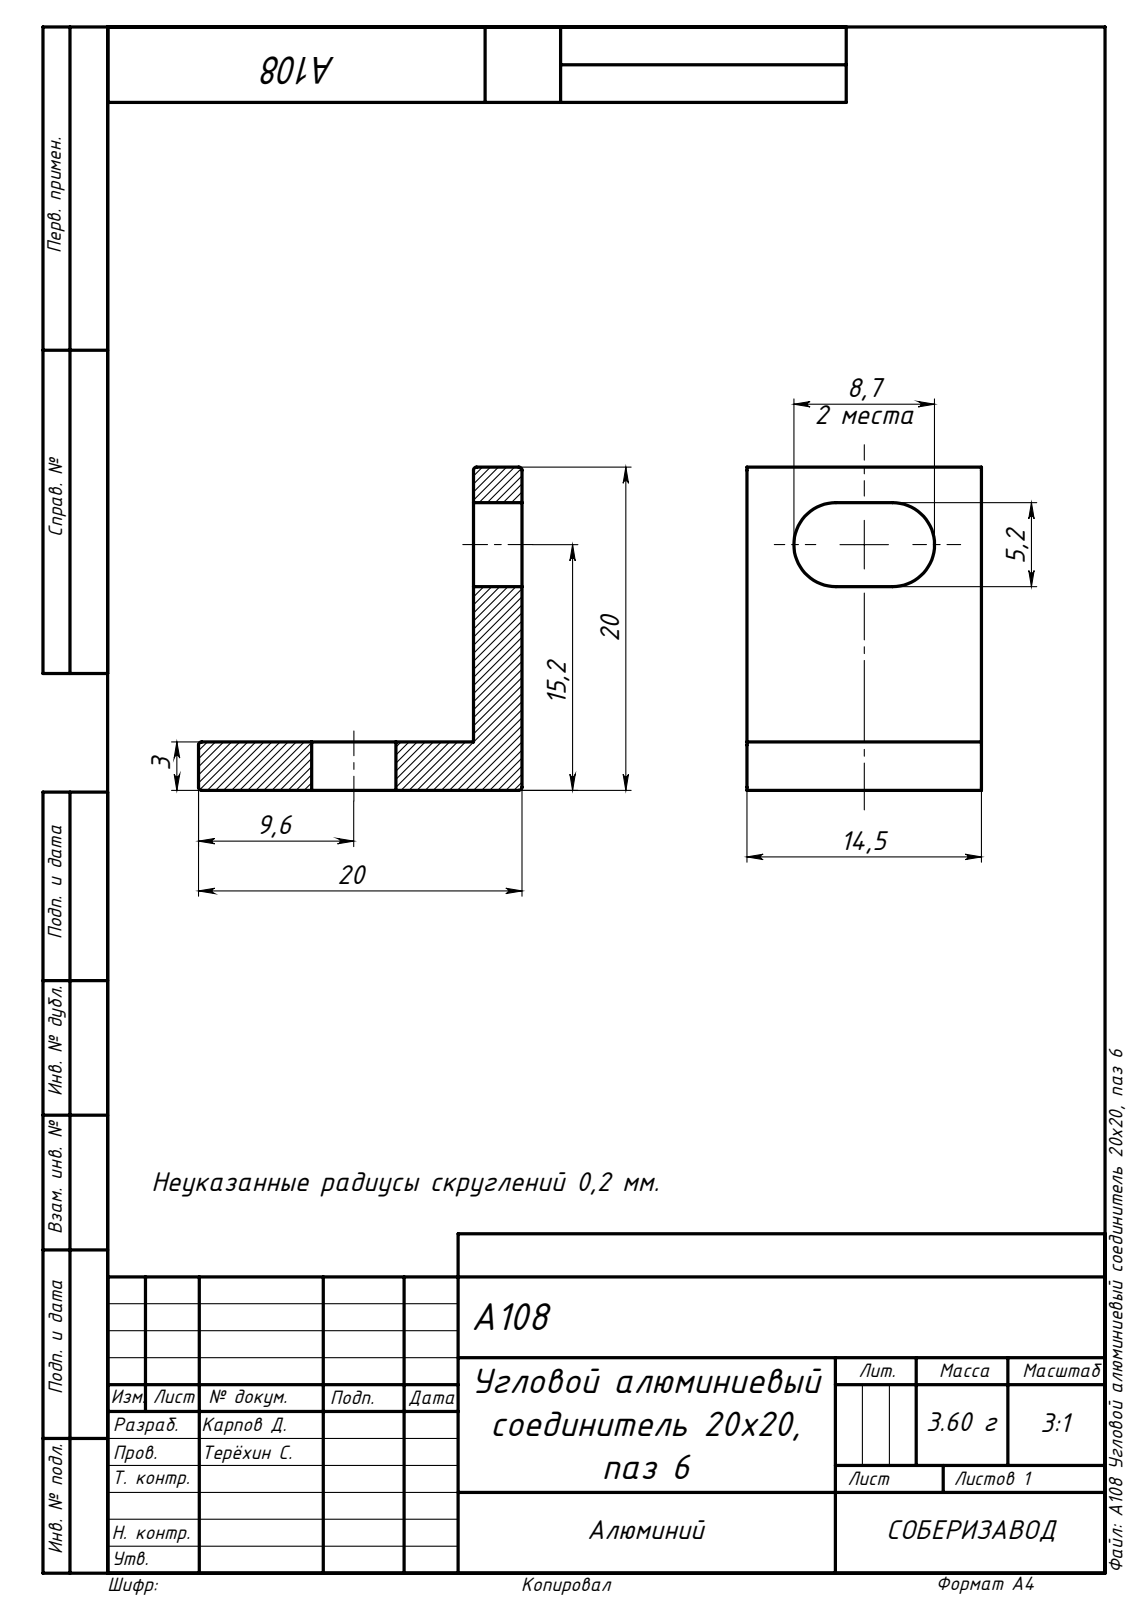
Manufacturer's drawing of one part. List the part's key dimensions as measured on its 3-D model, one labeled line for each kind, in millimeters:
Part name (STEP PRODUCT): A108 Угловой алюминиевый соединитель 20х20, паз 6
STEP written by: SolidWorks 2021 (AUTOMOTIVE_DESIGN)
Units: millimetres
Bodies: 1 solid, 22 faces (12 planar, 10 cylindrical, 0 other)
Overall size (bounding box): 20 × 20 × 14.5
Volume: 1 372 mm³ · Surface area: 1 358 mm²
Partial cylindrical surfaces — rounded edges, fillets, slot ends (radius × count): R0.2 ×5, R2.6 ×4
Main face-to-face distances: 3, 14.5, 17, 20, 5.2, 17.8, 14.8, 2.2, 12.6, 9.6
